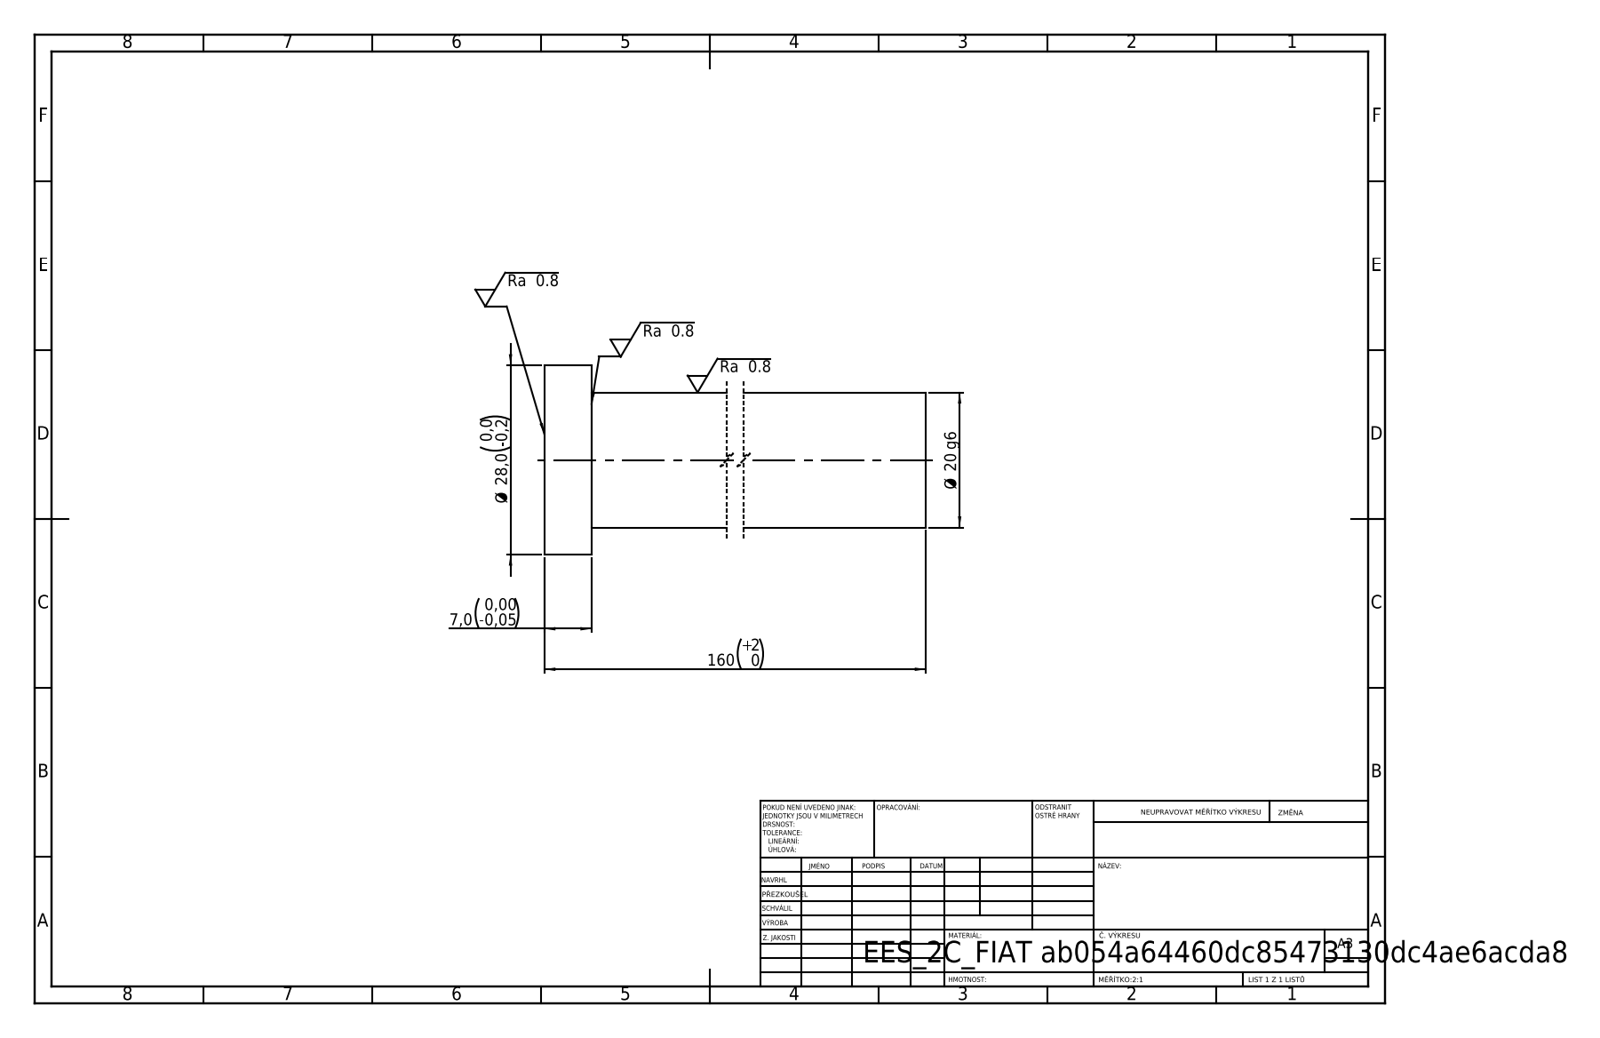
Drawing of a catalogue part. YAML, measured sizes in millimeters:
step_written_by: "SolidWorks 2019 (CONFIG_CONTROL_DESIGN)"
units: millimeters
bodies: {solids: 1, faces: 7, planar: 3, cylindrical: 4, other: 0}
overall_size: [160, 28, 28]
volume: 52377
surface_area: 11461
round_bosses_or_shafts:
  - {diameter: 28, count: 1}
  - {diameter: 20, count: 1}
face_to_face_distances: [160, 7, 153]
